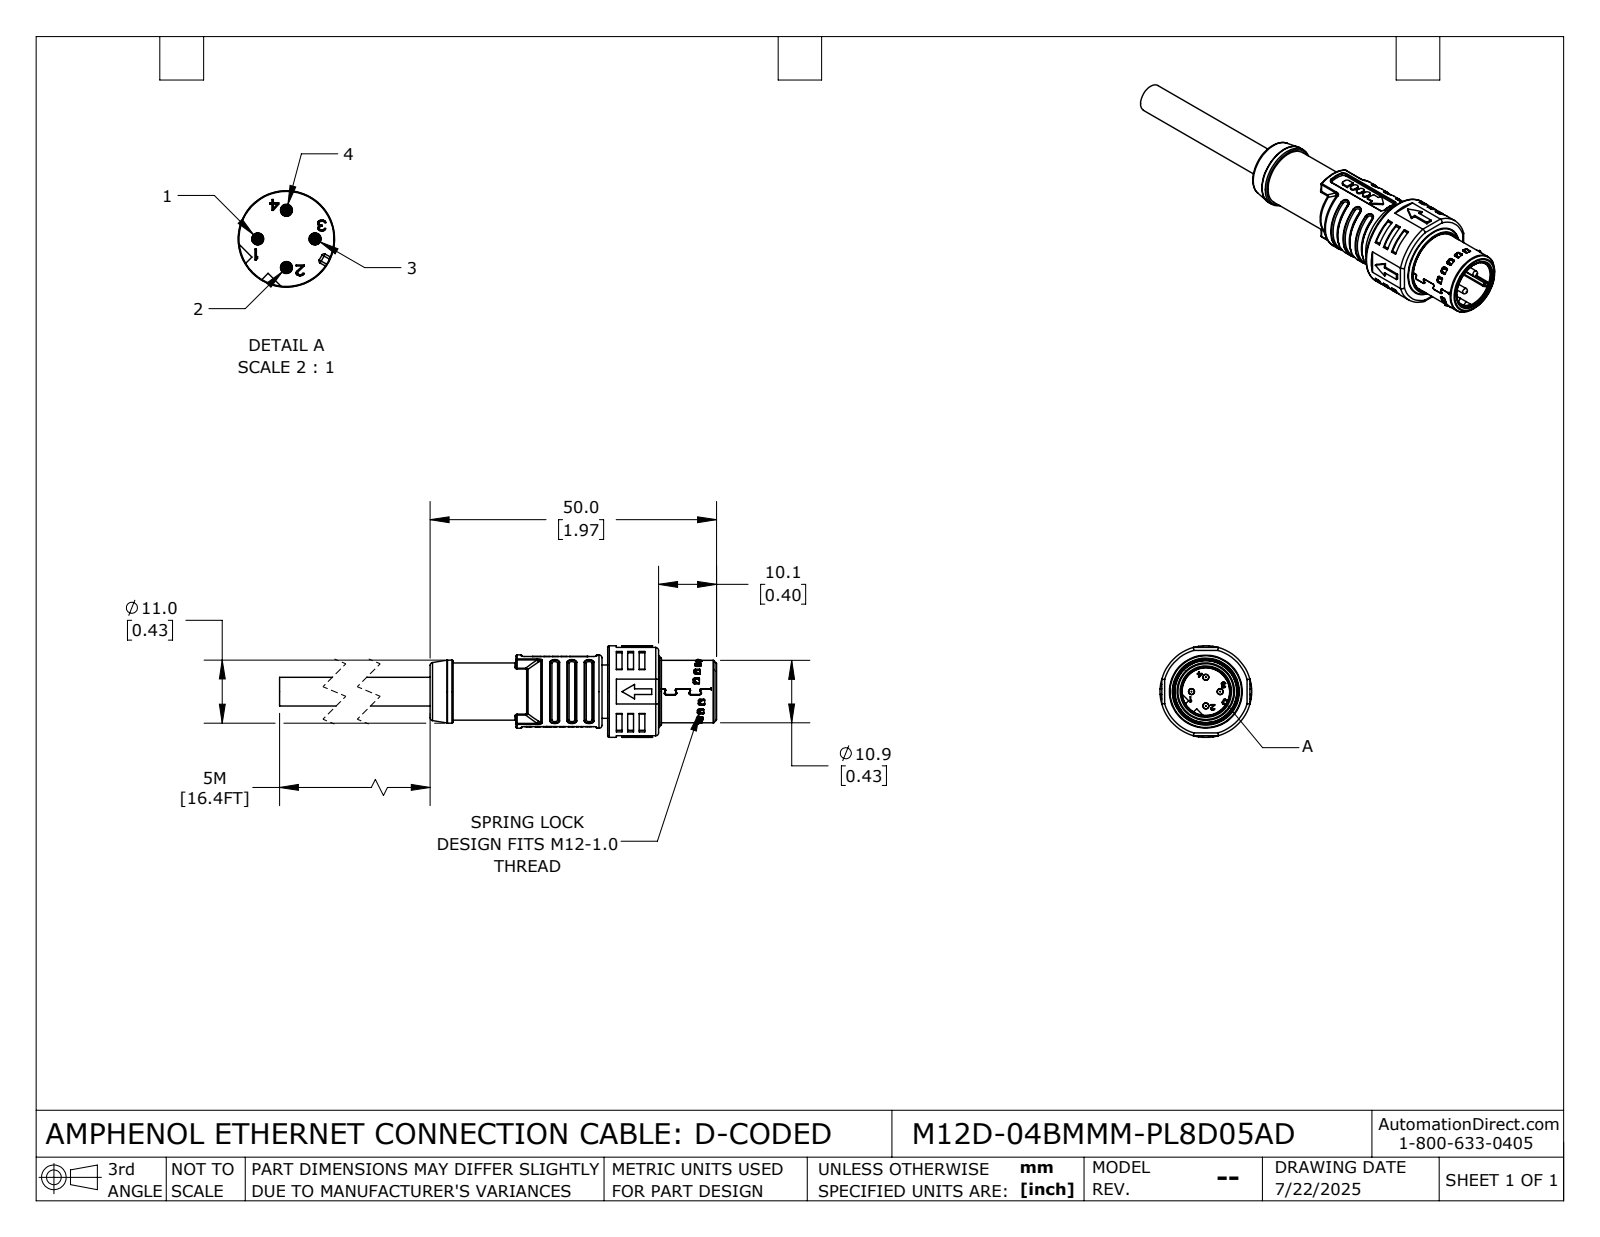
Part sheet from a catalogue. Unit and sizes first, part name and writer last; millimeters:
Units: millimetres
Overall size (bounding box): 80 × 16 × 16
Round holes (diameter × count): ⌀1.05 ×4, ⌀8.3 ×1, ⌀9 ×1, ⌀10.15 ×1, ⌀10.5 ×1, ⌀10.9 ×1, ⌀11.5 ×1, ⌀11.8 ×1, ⌀14.2 ×1
Round bosses / shafts (diameter × count): ⌀1 ×4, ⌀16 ×1, ⌀14.1 ×1, ⌀12.8 ×1, ⌀12.4 ×1, ⌀11 ×1, ⌀10.45 ×1, ⌀10.4 ×1
Partial cylindrical surfaces — rounded edges, fillets, slot ends (radius × count): R0.2 ×119, R0.25 ×66, R0.3 ×64, R0.15 ×44, R0.5 ×38, R0.13 ×12, R0.7 ×11, R0.1 ×7
Main face-to-face distances: 1, 30, 10.1, 8.9, 2.5, 1.2, 8.6, 32.5, 15.4, 1.5
Hole centre spacings: 2.5, 3.54, 5
Volume: 5 399 mm³ · Surface area: 5 961 mm²
Bodies: 1 solid, 2139 faces (996 planar, 644 cylindrical, 499 other)
Part name (STEP PRODUCT): M12D-04BMMM-PL8D05AD
STEP written by: SolidWorks 2024 (CONFIG_CONTROL_DESIGN)
